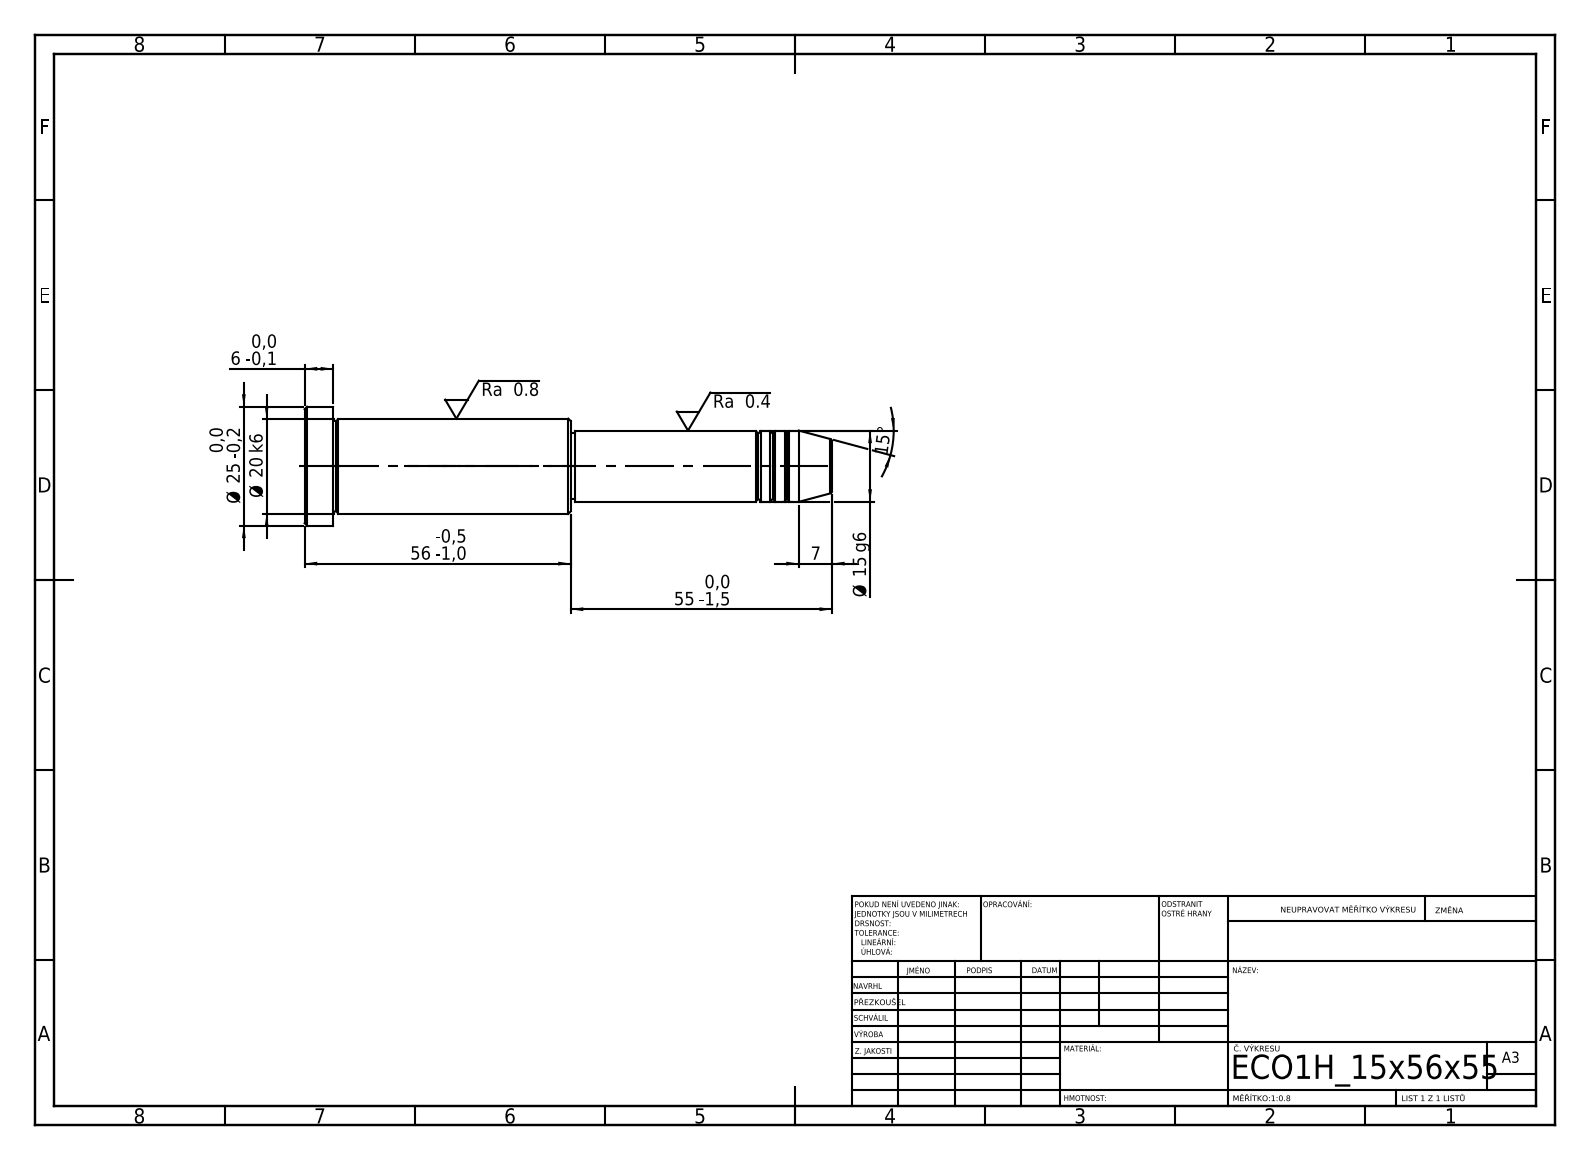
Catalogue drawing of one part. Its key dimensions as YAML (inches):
step_written_by: "SolidWorks 2019 (CONFIG_CONTROL_DESIGN)"
units: inches
bodies: {solids: 1, faces: 43, planar: 5, cylindrical: 14, other: 24}
overall_size: [4.37, 0.984, 0.984]
volume: 1.707
surface_area: 11.13
round_bosses_or_shafts:
  - {diameter: 0.984, count: 1}
  - {diameter: 0.787, count: 1}
  - {diameter: 0.591, count: 1}
  - {diameter: 0.551, count: 1}
face_to_face_distances: [0.236, 1.969, 2.205, 2.165, 4.134, 4.37, 2.126, 0.039, 2.008, 2.244]
